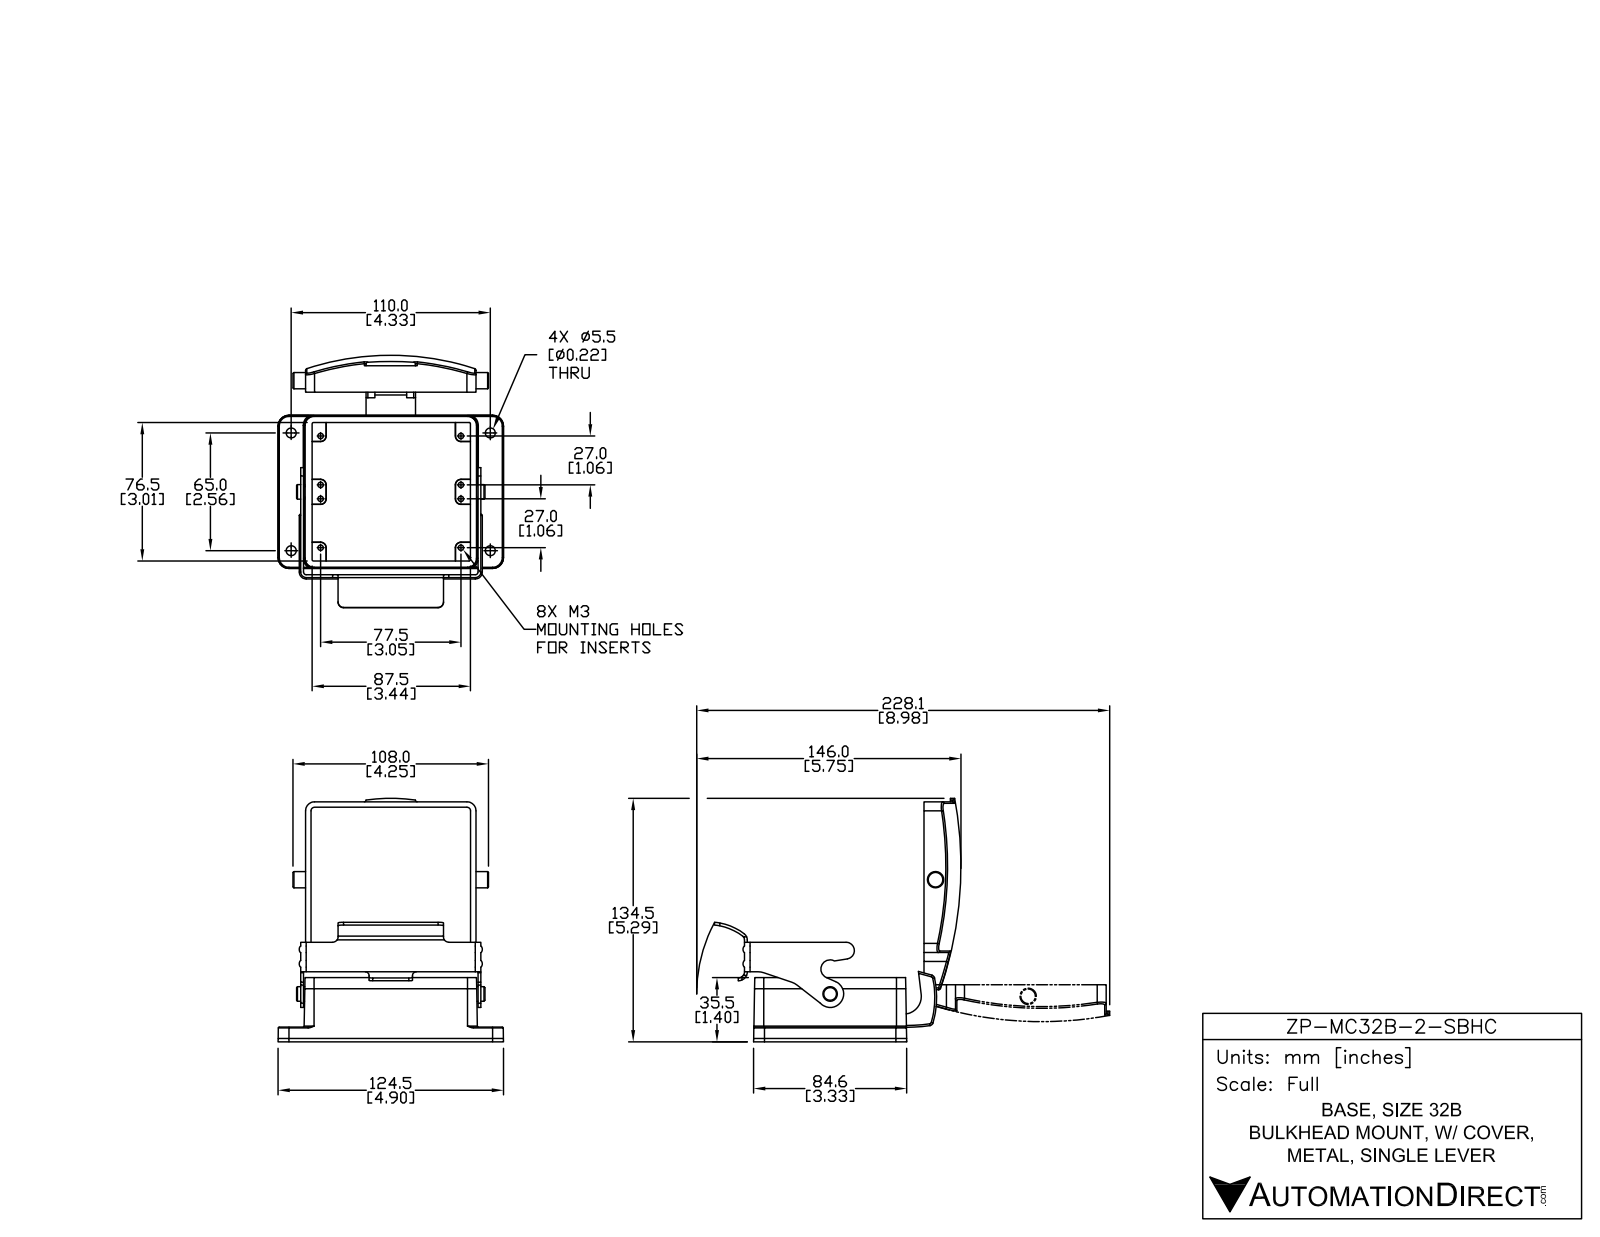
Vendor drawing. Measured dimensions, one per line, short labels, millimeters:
name: ZP-MC32B-2-SBHC
written by: SolidWorks 2014 (AUTOMOTIVE_DESIGN)
unit: mm
bodies: 2 solids, 364 faces (138 planar, 136 cylindrical, 90 other)
size: 139.39 × 134.29 × 124
volume: 131 019 mm³; area: 74 312 mm²
holes: 9× ⌀3, 4× ⌀5.5
bosses: 1× ⌀9, 1× ⌀8
rounds: 10× R2, 7× R1, 6× R0.5, 6× R5, 4× R0.75, 4× R3, 4× R6, 2× R1.5
face distances: 3, 1.56, 75.25, 86.25, 8.2, 97.96, 80.15, 35.3, 83.6, 8.35
hole spacings: 16.33, 27, 32.94, 34.7, 39.82, 65.4, 77.5, 82.07
